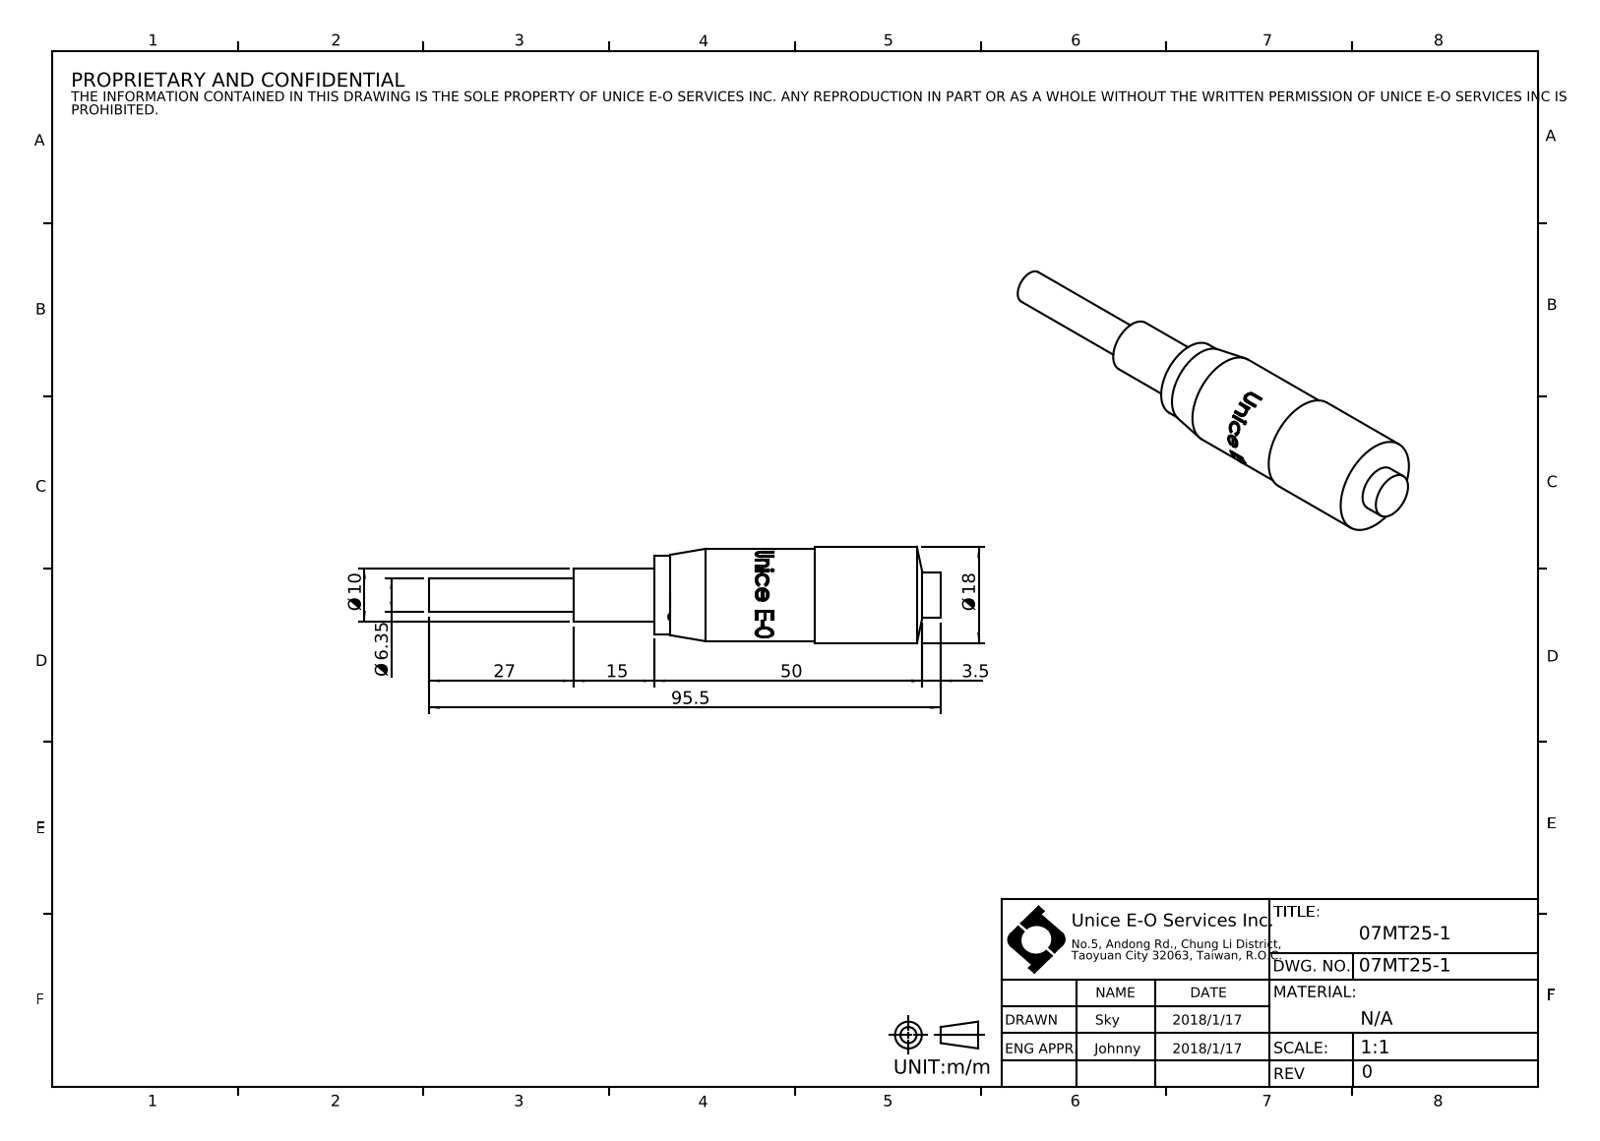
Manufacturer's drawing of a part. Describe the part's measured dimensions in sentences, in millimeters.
The part is named "07MT25-1". Its 3-D file was written by "SolidWorks 2016 (AUTOMOTIVE_DESIGN)". It is 0 solids with 74 faces: 18 planar, 25 cylindrical and 31 other. Overall it measures 95.5 by 18 by 18 millimeters. Round bosses or shafts: 1 of diameter 18, 1 of diameter 17.2, 1 of diameter 14.7, 1 of diameter 10, 1 of diameter 8.5, 1 of diameter 6.35. Partial cylindrical surfaces (rounded edges, fillets, slot ends): 1 of radius 8.55. The main face-to-face distances are 53.5, 15, 68.5, 27, 42, 95.5, 45, 72, 30, 23.5.
